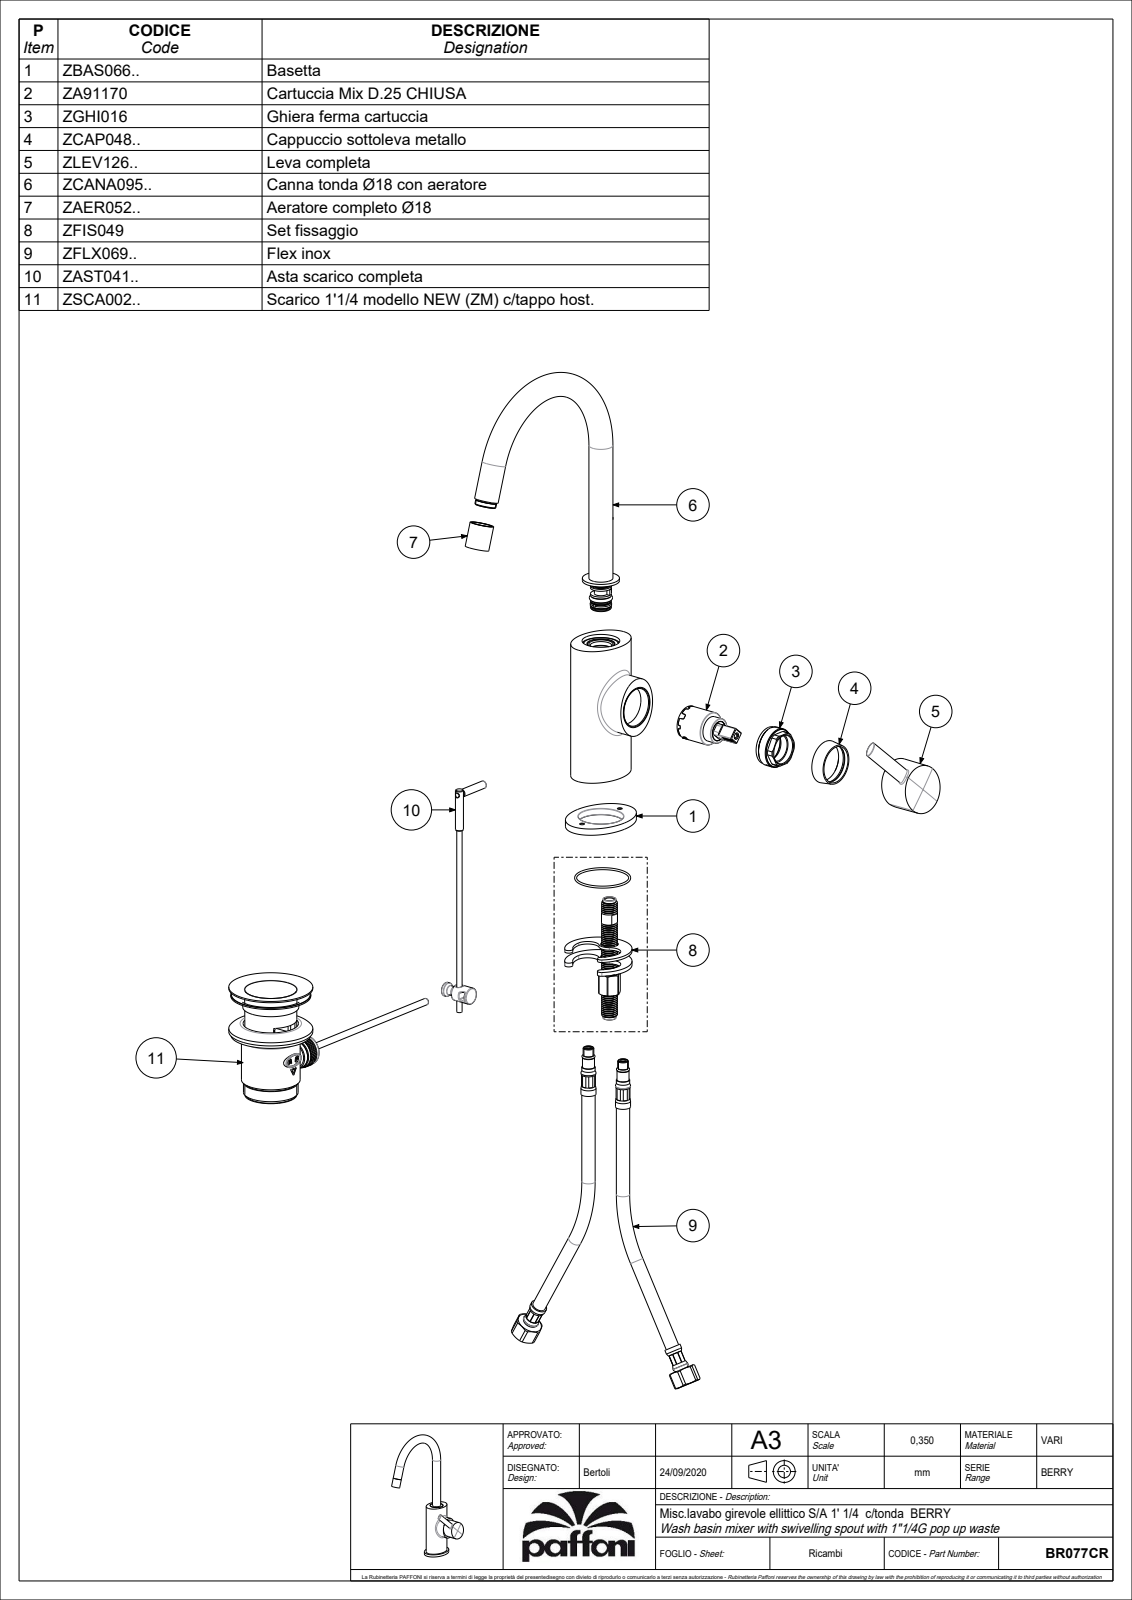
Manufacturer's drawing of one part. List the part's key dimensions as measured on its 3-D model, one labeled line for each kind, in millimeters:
Part name (STEP PRODUCT): BR077CR
STEP written by: CREO PARAMETRIC BY PTC INC, 2020044 (CONFIG_CONTROL_DESIGN)
Units: millimetres
Bodies: 5 solids, 1475 faces (600 planar, 569 cylindrical, 306 other)
Overall size (bounding box): 289.1 × 185.93 × 83.2
Volume: 213 115 mm³ · Surface area: 96 736 mm²
Round holes (diameter × count): ⌀0.5 ×51, ⌀5 ×4, ⌀6 ×4, ⌀3 ×2, ⌀4 ×2, ⌀4.5 ×2, ⌀5.5 ×2, ⌀9.4 ×2, ⌀15 ×2, ⌀16 ×2, ⌀3.3 ×1, ⌀7 ×1
Round bosses / shafts (diameter × count): ⌀18 ×3, ⌀15.9 ×2, ⌀12 ×2, ⌀10 ×2, ⌀9 ×2, ⌀4 ×2, ⌀38.8 ×1, ⌀28.5 ×1
Partial cylindrical surfaces — rounded edges, fillets, slot ends (radius × count): R0.5 ×40, R0.3 ×17, R1 ×15, R0.2 ×13, R0.15 ×10, R2 ×10, R1.25 ×4, R2.45 ×4
Main face-to-face distances: 110, 5, 3, 8, 2, 7, 105, 1.9, 102, 0.5
Hole centre spacings: 3.35, 1.5, 2.12, 3, 4.74, 5.41, 7.5, 8.08
